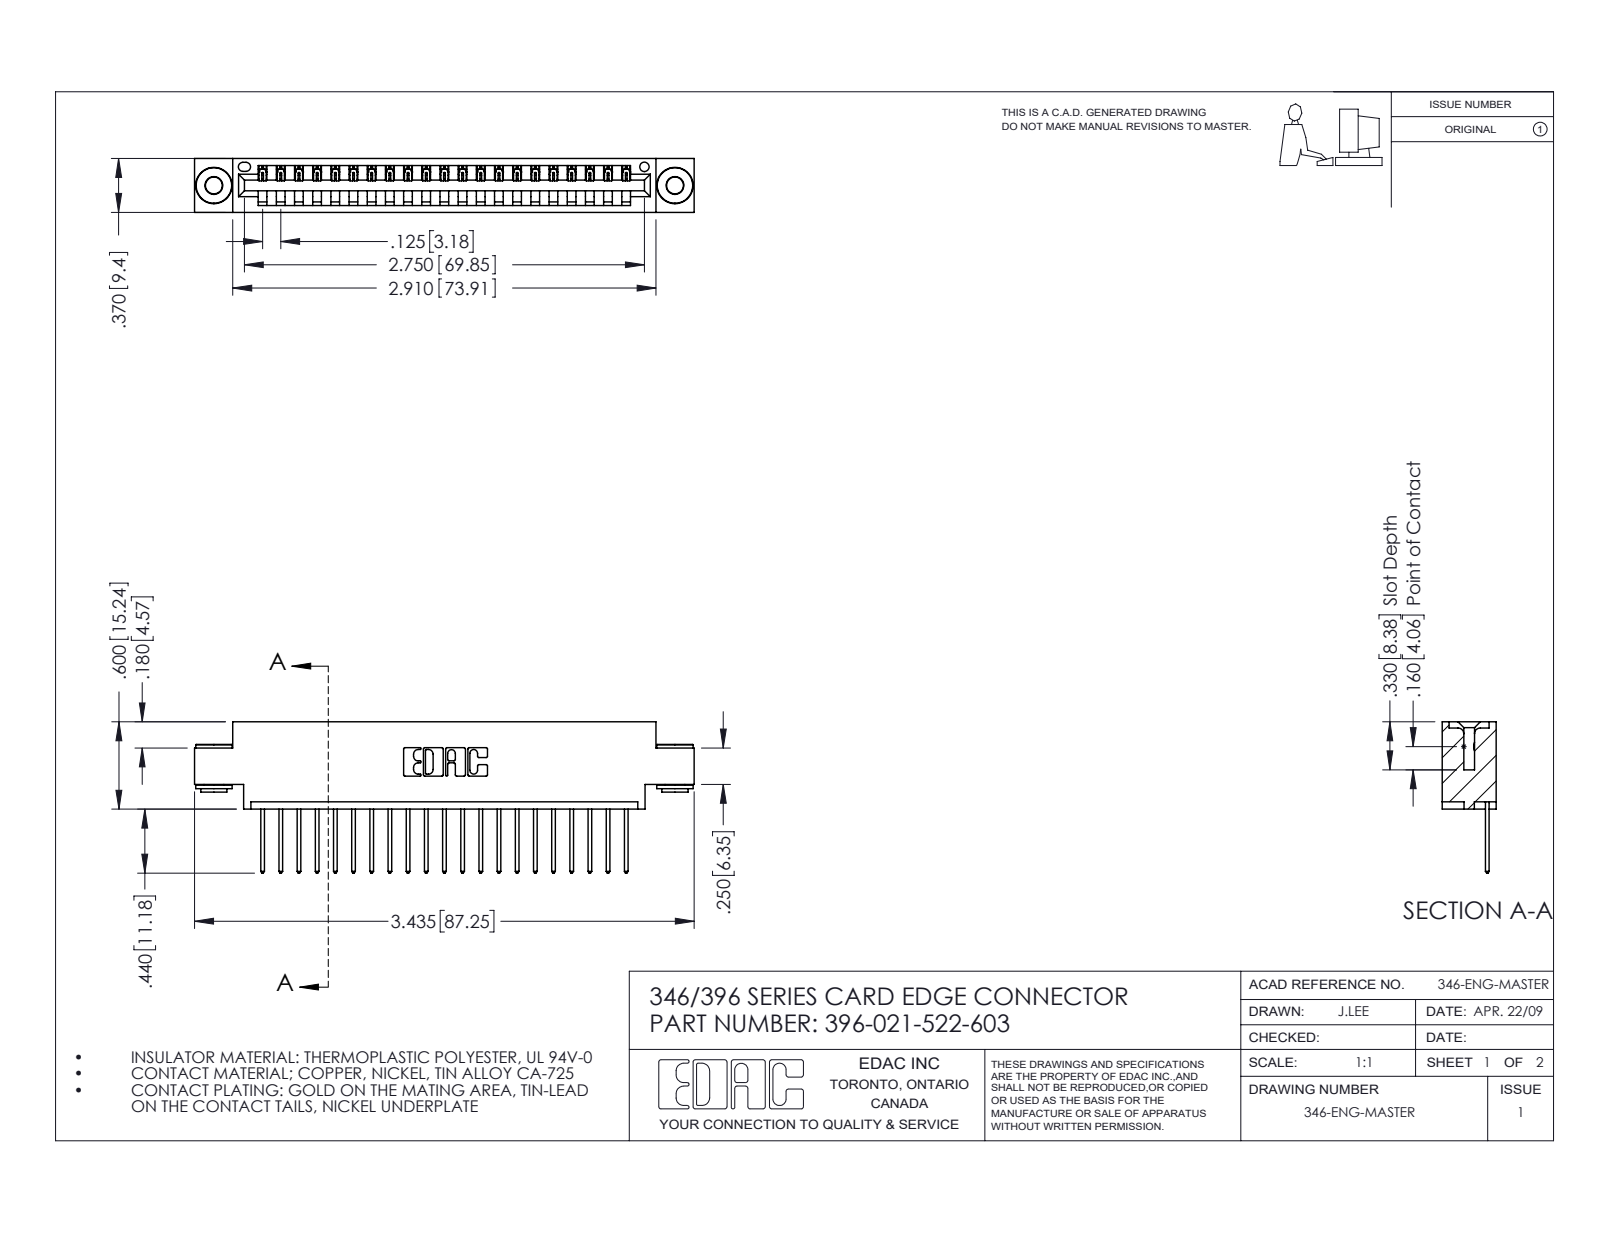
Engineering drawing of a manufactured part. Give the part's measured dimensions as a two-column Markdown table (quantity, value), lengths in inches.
| quantity | value |
| --- | --- |
| part name | 345-250-002_345-250-002-102; 396-021-522-603; 345-292-001_345-293-122; 346 Part_0.170 Offset - 0.156 Dia-TH |
| STEP written by | SolidWorks 2016 (CONFIG_CONTROL_DESIGN) |
| units | inches |
| bodies | 24 solids, 1382 faces (930 planar, 444 cylindrical, 8 other) |
| overall size | 3.435 × 1.04 × 0.37 |
| volume | 0.493 in³ |
| surface area | 16 in² |
| round holes (diameter × count) | 0.116 × 2, 0.156 × 2, 0.064 × 1 |
| round bosses / shafts (diameter × count) | 0.25 × 2, 0.18 × 2, 0.136 × 2 |
| partial cylindrical surfaces (radius × count) | 0.006 × 42, 0.01 × 42, 0.01 × 22, 0.007 × 6, 0.031 × 6, 0.026 × 3, 0.031 × 2, 0.04 × 2 |
| main face-to-face distances | 0.048, 0.322, 0.37, 0.25, 0.025, 0.072, 0.298, 0.148, 0.222, 0.1 |
| hole center spacings | 0.246, 2.963, 3.17 |
